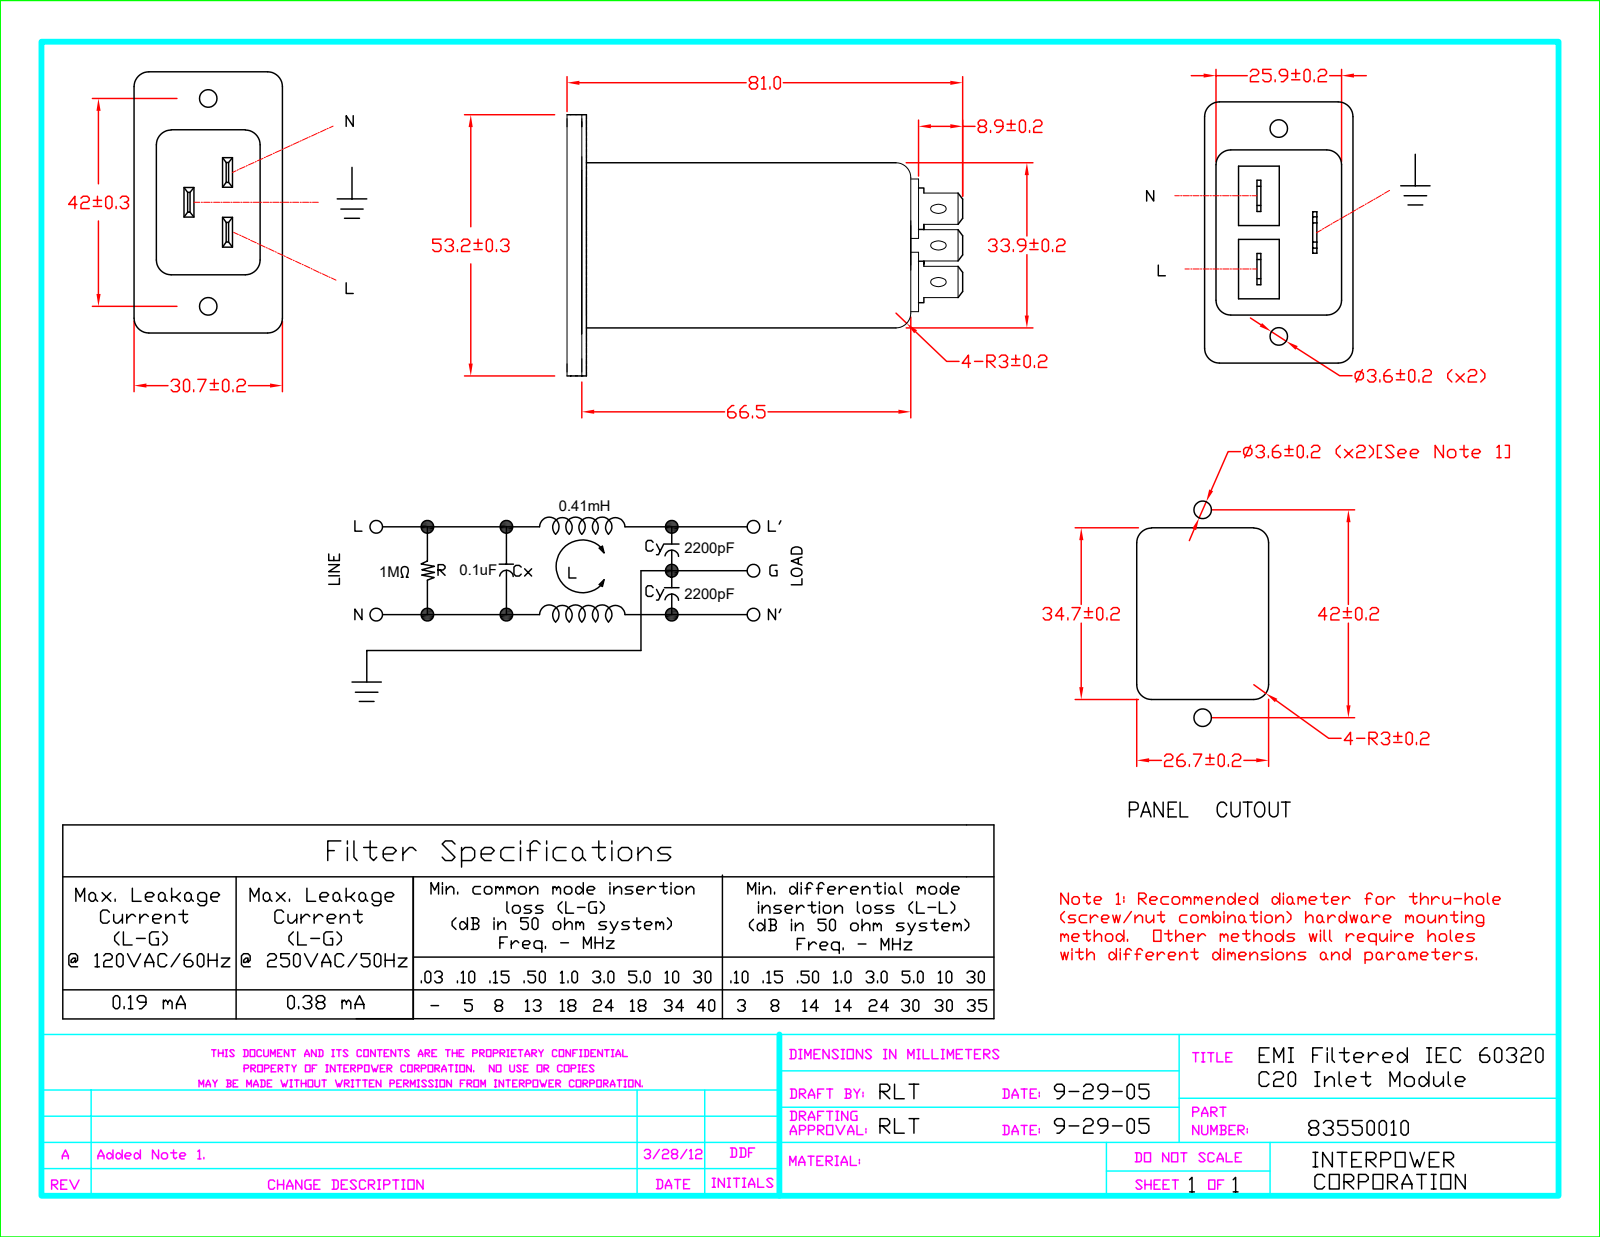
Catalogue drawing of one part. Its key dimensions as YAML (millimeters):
part_name: "83550010"
step_written_by: "SolidWorks 2007 (CONFIG_CONTROL_DESIGN)"
units: millimeters
bodies: {solids: 1, faces: 156, planar: 94, cylindrical: 40, other: 22}
overall_size: [81, 53.2, 30.7]
volume: 53171
surface_area: 15681
round_holes:
  - {diameter: 3.45, count: 2}
partial_cylinders:
  - {radius: 3, count: 12}
  - {radius: 0.25, count: 8}
  - {radius: 5, count: 8}
face_to_face_distances: [25.9, 33.9, 2.45, 23.45, 4, 3.5, 0.5, 0.71, 1.21, 4.71]
hole_center_spacings: [42]
